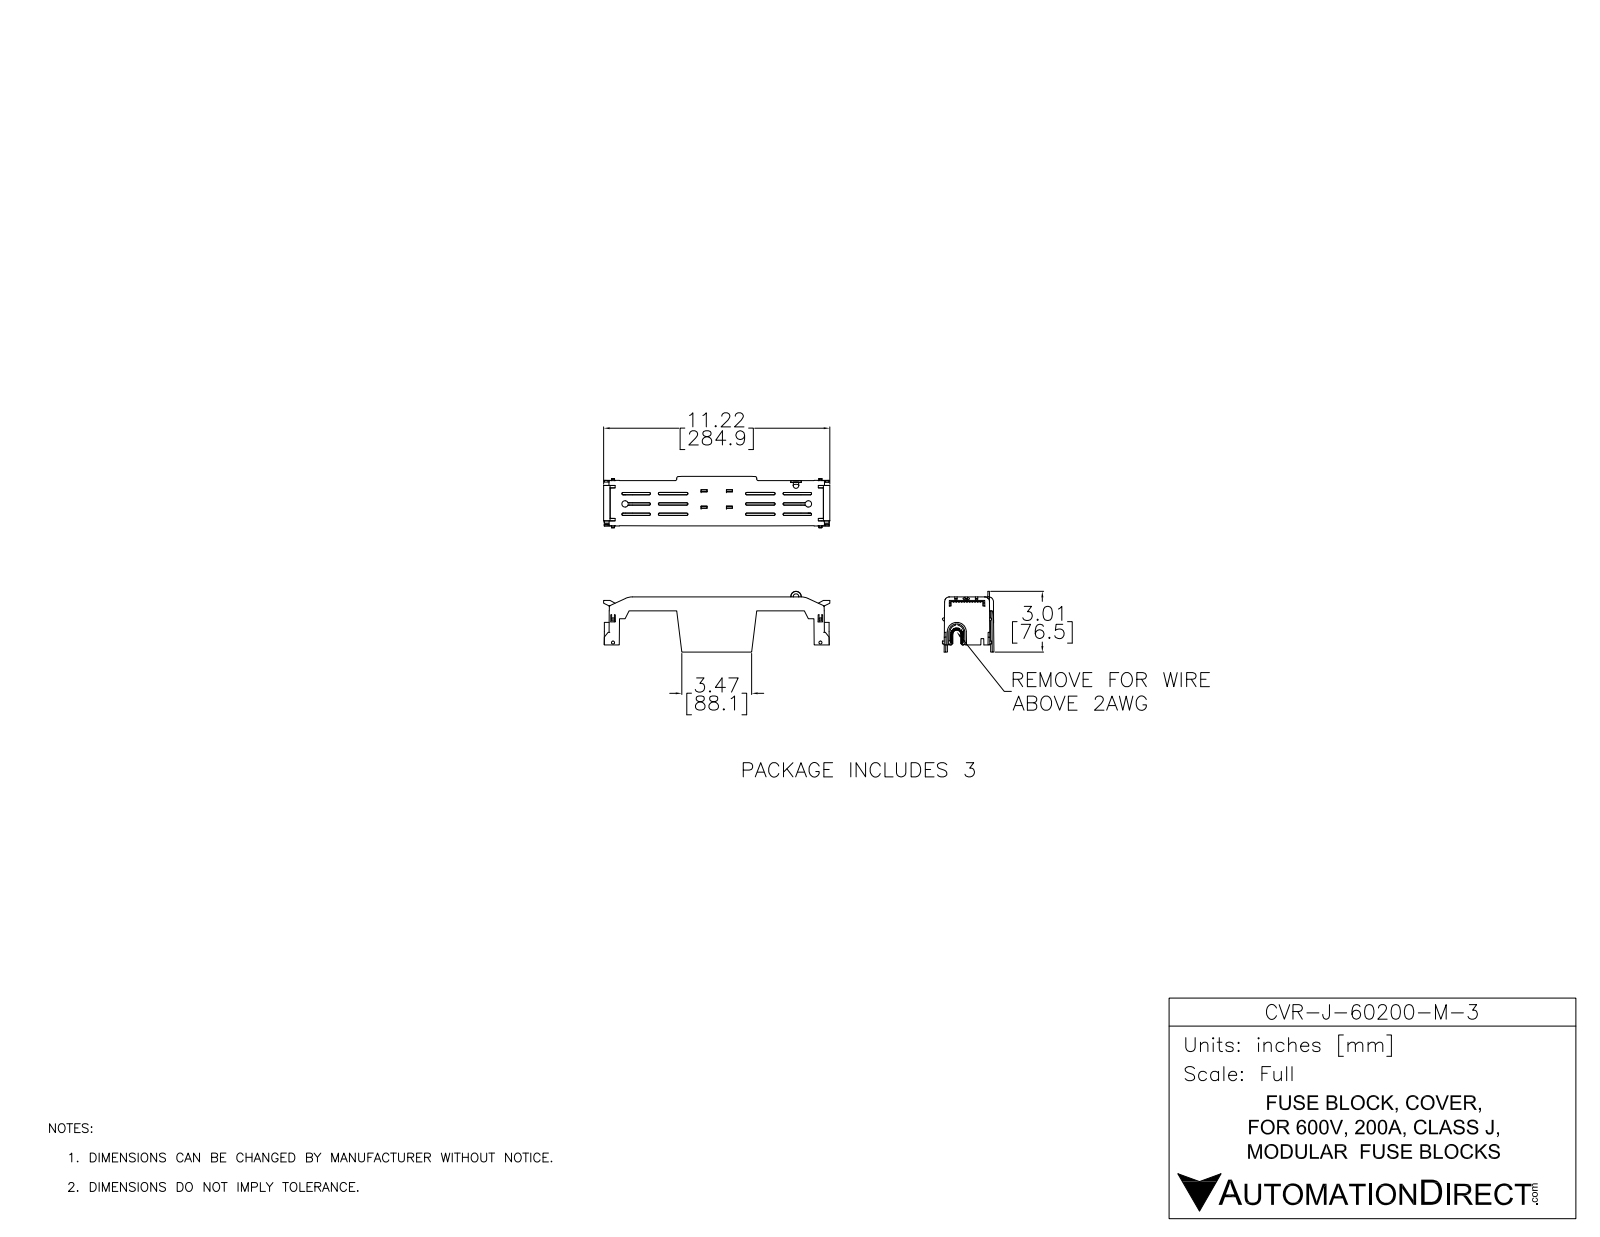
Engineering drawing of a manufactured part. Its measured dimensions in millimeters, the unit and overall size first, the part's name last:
Units: millimetres
Overall size (bounding box): 186.4 × 76.6 × 64.8
Round holes (diameter × count): ⌀7 ×1
Partial cylindrical surfaces — rounded edges, fillets, slot ends (radius × count): R1 ×12, R6 ×9, R3 ×8, R4 ×7, R0.9 ×6, R1.5 ×4, R0.3 ×2, R0.5 ×2
Main face-to-face distances: 2, 5, 3, 7, 13, 15.4, 2.4, 4.4, 20.4, 6.5
Volume: 57 260 mm³ · Surface area: 61 860 mm²
Bodies: 1 solid, 1408 faces (920 planar, 113 cylindrical, 375 other)
Part name (STEP PRODUCT): CVR-J-60200-M-3
STEP written by: SolidWorks 2017 (AUTOMOTIVE_DESIGN)
